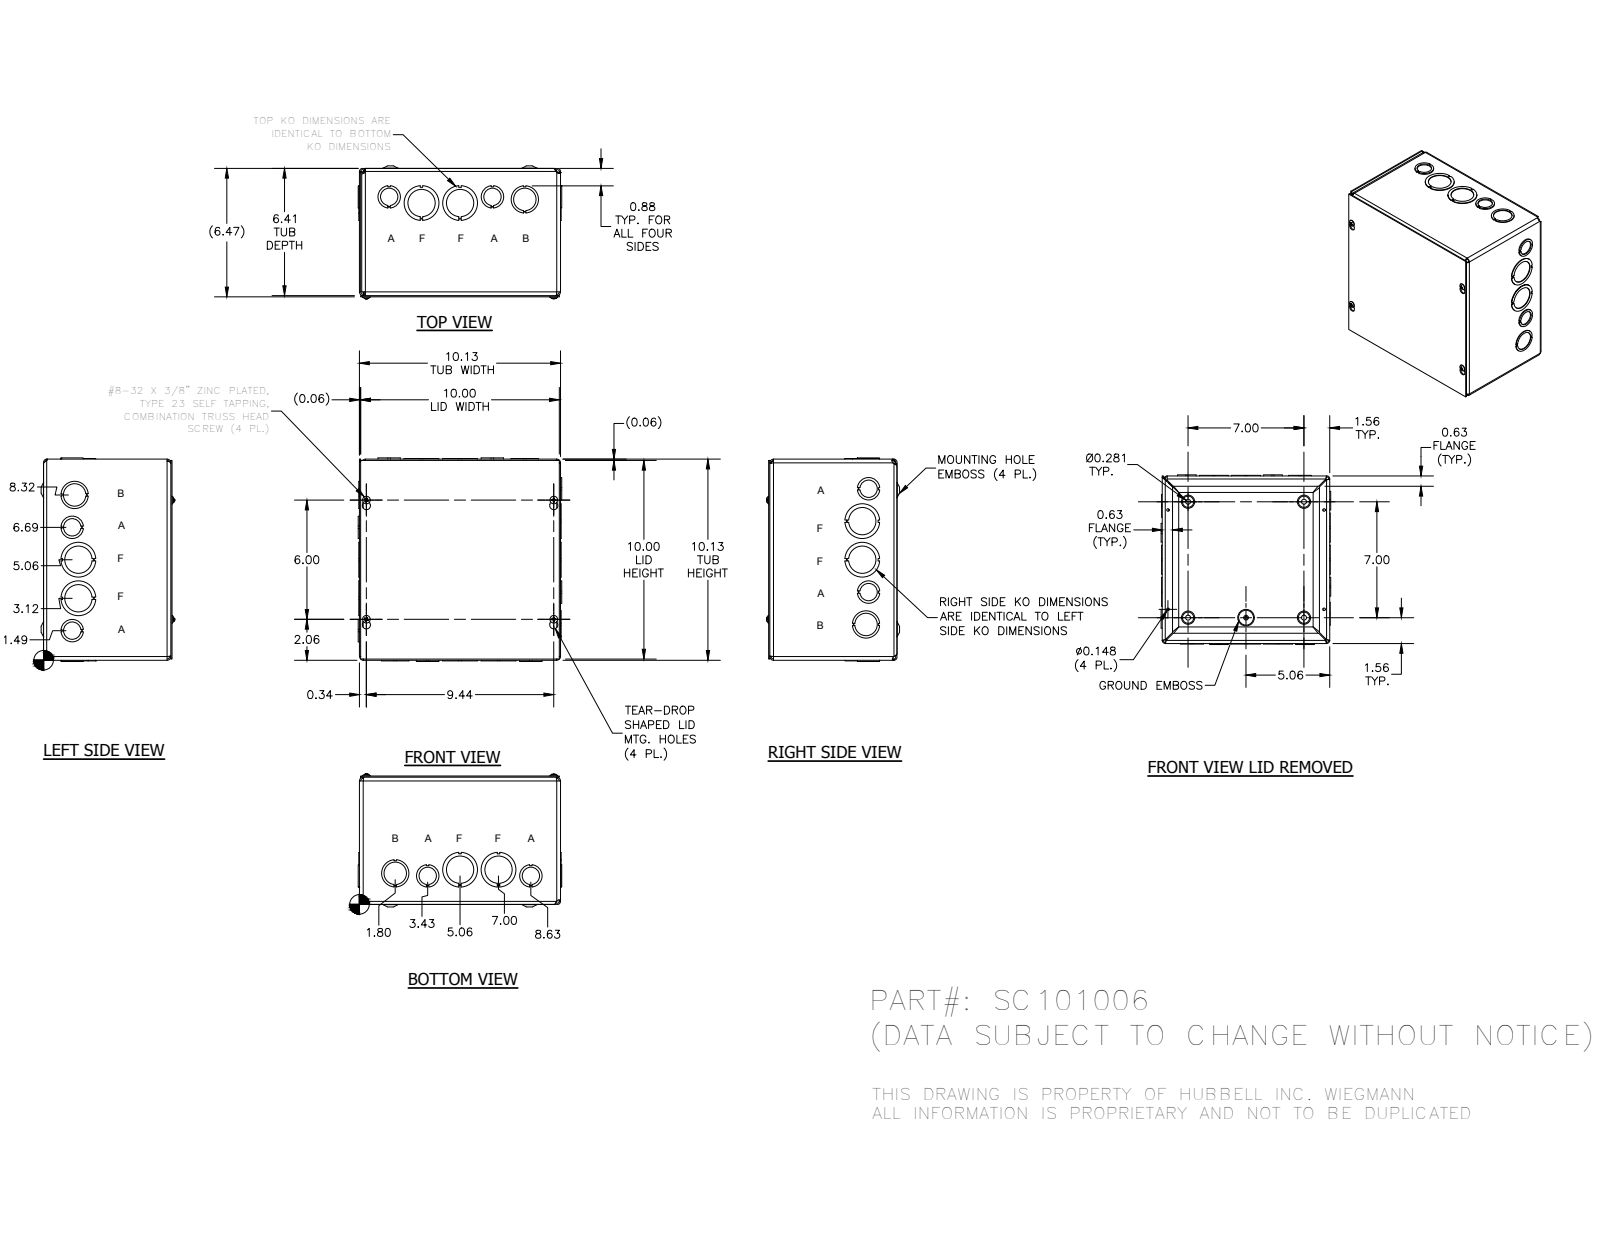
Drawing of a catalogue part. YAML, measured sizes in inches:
part_name: "SC1010BKP; SC101006WRA; SC1010LID; 34056 (+1 more)"
step_written_by: "Autodesk Inventor 2014 (AUTOMOTIVE_DESIGN)"
units: inches
bodies: {solids: 22, faces: 918, planar: 573, cylindrical: 187, other: 158}
overall_size: [10.249, 10.249, 6.693]
round_holes:
  - {diameter: 1.125, count: 12}
  - {diameter: 1.375, count: 10}
  - {diameter: 0.875, count: 8}
  - {diameter: 1.75, count: 6}
  - {diameter: 0.148, count: 4}
  - {diameter: 0.3, count: 4}
  - {diameter: 0.165, count: 1}
round_bosses_or_shafts:
  - {diameter: 0.384, count: 4}
  - {diameter: 0.164, count: 4}
  - {diameter: 0.228, count: 1}
partial_cylinders:
  - {radius: 0.125, count: 12}
  - {radius: 0.187, count: 8}
  - {radius: 0.055, count: 4}
  - {radius: 0.062, count: 4}
  - {radius: 0.094, count: 4}
  - {radius: 0.117, count: 4}
  - {radius: 0.124, count: 4}
  - {radius: 0.156, count: 4}
face_to_face_distances: [0.062, 0.062, 6.343, 10.125, 10.063, 10.063, 10.001, 6.405, 0.063, 6.406]
hole_center_spacings: [1.659, 1.94, 3.584, 1.333, 5.2, 5.204, 6.613, 7]
